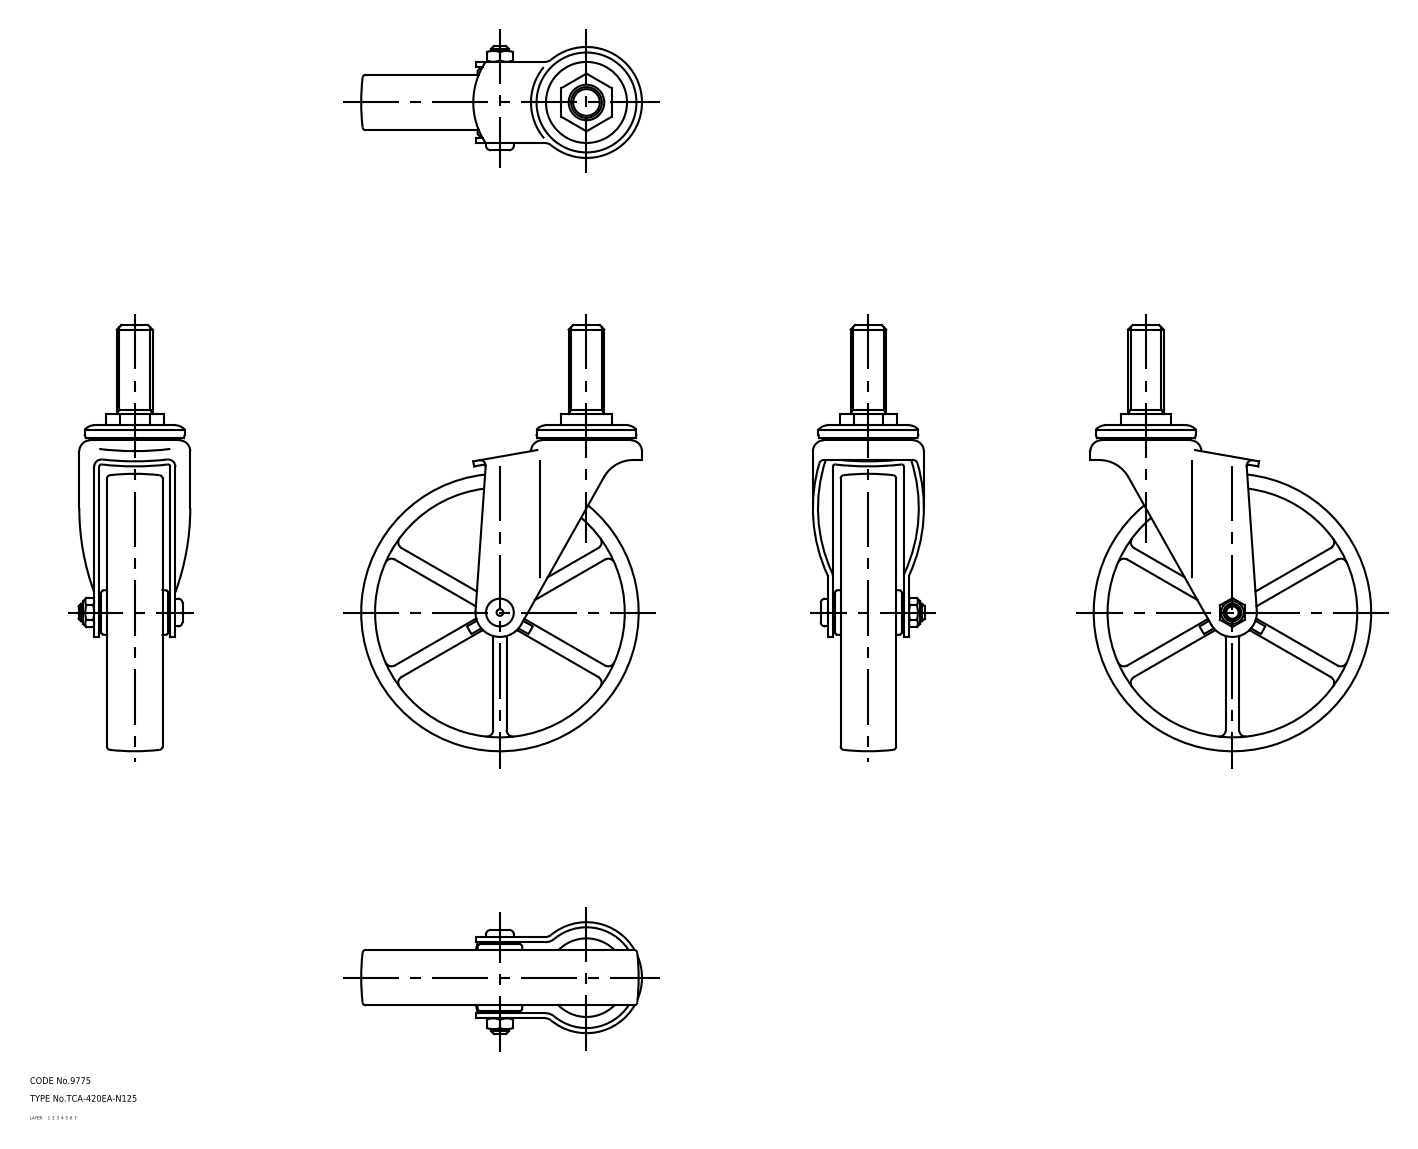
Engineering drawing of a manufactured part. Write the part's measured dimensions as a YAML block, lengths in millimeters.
part_name: "wheel; mounting plate; main shaft; axle (+1 more)"
step_written_by: "CADfix (AUTOMOTIVE_DESIGN)"
units: millimeters
bodies: {solids: 5, faces: 500, planar: 0, cylindrical: 0, other: 500}
overall_size: [192, 126.5, 50.3]
volume: 265396
surface_area: 71817
